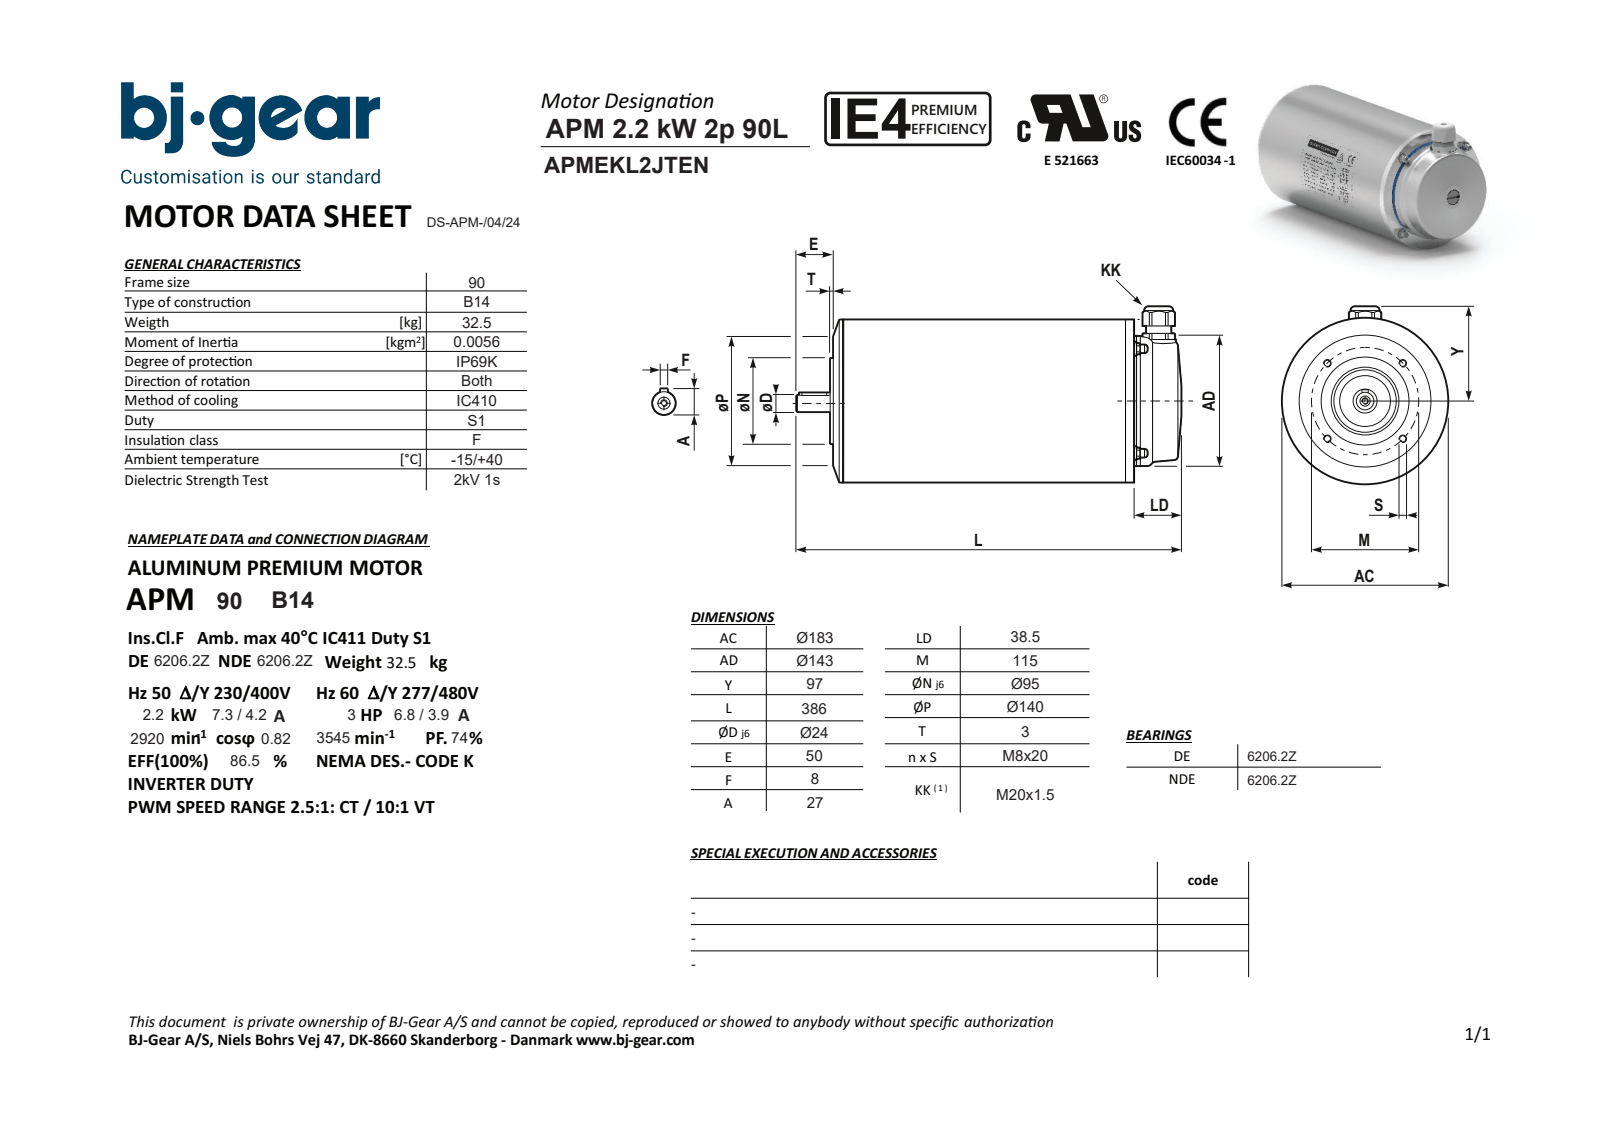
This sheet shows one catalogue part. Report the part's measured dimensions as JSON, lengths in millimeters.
{"part_name": "APMEKL2JTENN4KCR2-N---NNN", "step_written_by": "Solid Edge (AUTOMOTIVE_DESIGN)", "units": "millimeters", "bodies": {"solids": 1, "faces": 156, "planar": 75, "cylindrical": 50, "other": 31}, "overall_size": [386, 187.3, 182.6], "volume_mm3": 8327000, "surface_area_mm2": 247972, "round_holes": [[6.65, 5], [8.4, 1], [16, 1], [28, 1], [82, 1]], "round_bosses_or_shafts": [[11.5, 4], [7, 4], [182.6, 1], [182.6, 1], [143, 1], [95, 1], [30, 1], [24, 1]], "partial_cylinders_radius": [[4, 2], [13.2, 1]], "face_to_face_distances": [297.5, 6, 291.5, 3, 9, 300.5, 8, 336, 38.5, 330], "hole_center_spacings": [57.5, 81.32, 115]}
